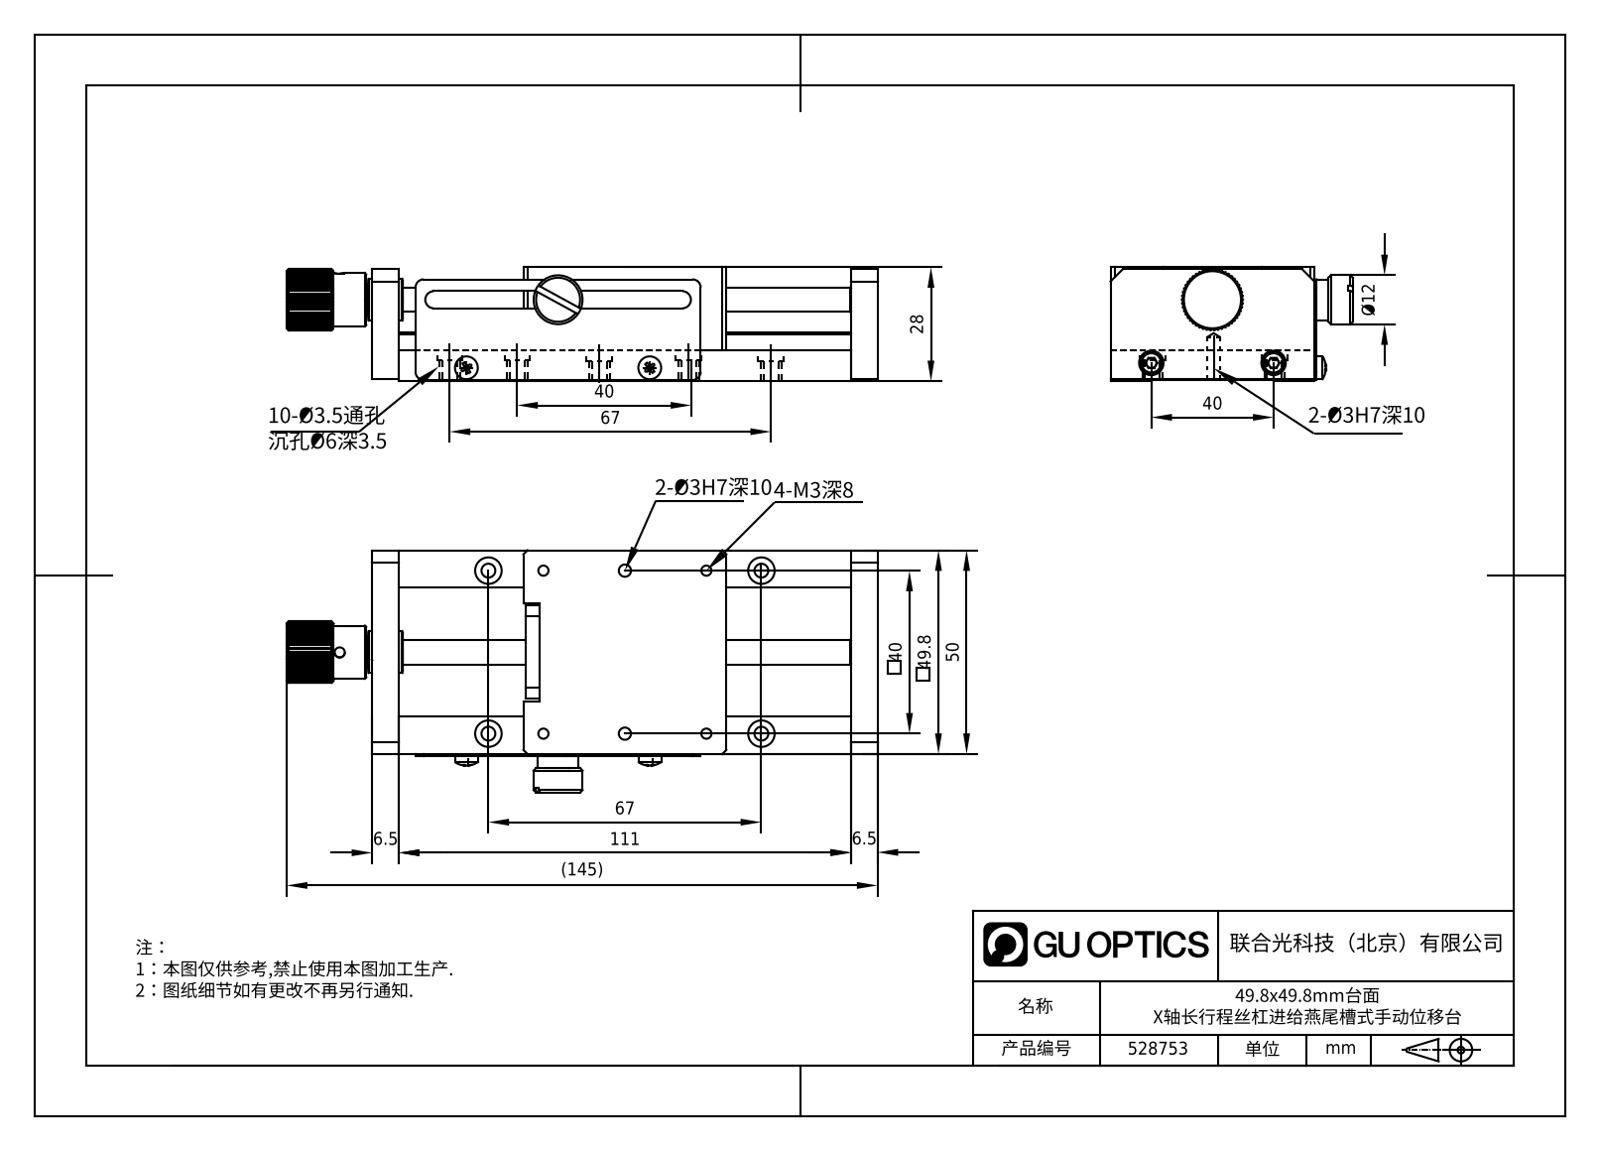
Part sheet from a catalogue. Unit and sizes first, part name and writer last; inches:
Units: inches
Overall size (bounding box): 5.709 × 2.341 × 1.102
Round holes (diameter × count): ⌀0.098 ×12, ⌀0.134 ×12, ⌀0.256 ×10, ⌀0.081 ×6, ⌀0.118 ×5, ⌀0.114 ×4, ⌀0.197 ×4, ⌀0.236 ×3, ⌀0.059 ×2, ⌀0.122 ×2, ⌀0.13 ×1, ⌀0.138 ×1
Round bosses / shafts (diameter × count): ⌀0.177 ×4, ⌀0.118 ×4, ⌀0.098 ×4, ⌀0.22 ×2, ⌀0.217 ×2, ⌀0.512 ×1, ⌀0.472 ×1, ⌀0.406 ×1
Partial cylindrical surfaces — rounded edges, fillets, slot ends (radius × count): R0.012 ×8, R0.079 ×4, R0.083 ×2, R0.295 ×1, R0.453 ×1
Main face-to-face distances: 0.472, 0.177, 0.465, 0.287, 0.295, 0.256, 1.094, 4.626, 0.63, 0.807
Hole centre spacings: 0.787, 1.575, 0.335, 0.531, 0.95, 1.319, 1.536, 1.662
Bodies: 0 solids, 750 faces (373 planar, 192 cylindrical, 185 other)
Part name (STEP PRODUCT): 528753
STEP written by: SolidWorks 2020 (CONFIG_CONTROL_DESIGN)
